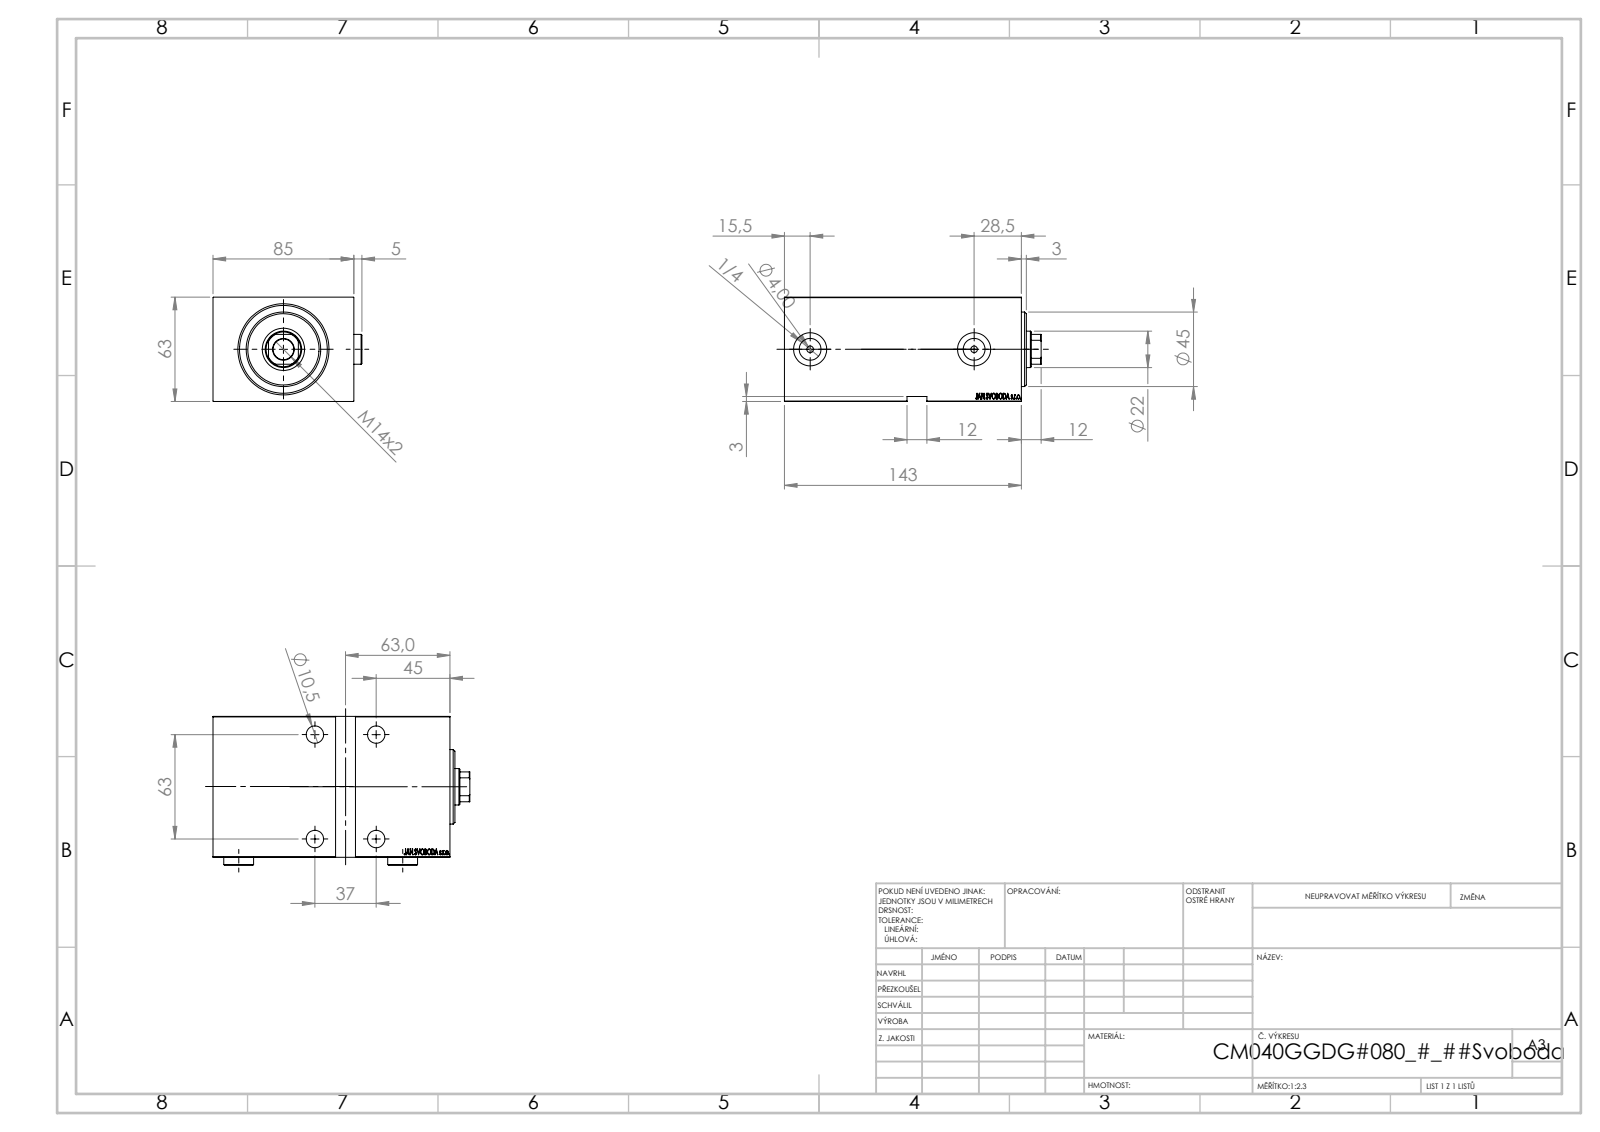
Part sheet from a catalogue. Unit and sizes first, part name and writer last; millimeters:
Units: millimetres
Overall size (bounding box): 155 × 89.9 × 63
Round holes (diameter × count): ⌀10.5 ×4, ⌀16.5 ×4, ⌀4 ×2, ⌀13.16 ×2, ⌀20 ×2, ⌀12.5 ×1, ⌀22 ×1, ⌀25.5 ×1, ⌀40 ×1, ⌀42 ×1, ⌀53 ×1
Round bosses / shafts (diameter × count): ⌀18 ×2, ⌀45 ×1, ⌀27 ×1
Partial cylindrical surfaces — rounded edges, fillets, slot ends (radius × count): R10.5 ×1
Main face-to-face distances: 63, 85, 143, 12, 131, 5, 138, 126, 3, 60
Hole centre spacings: 37, 63, 73.06, 99
Volume: 656 084 mm³ · Surface area: 105 029 mm²
Bodies: 5 solids, 915 faces (447 planar, 70 cylindrical, 398 other)
Part name (STEP PRODUCT): V450CM_VC_G; Zatka_OIL_PORT; V450CM_G_VCP; V450CM_G_Body
STEP written by: SolidWorks 2019 (CONFIG_CONTROL_DESIGN)
